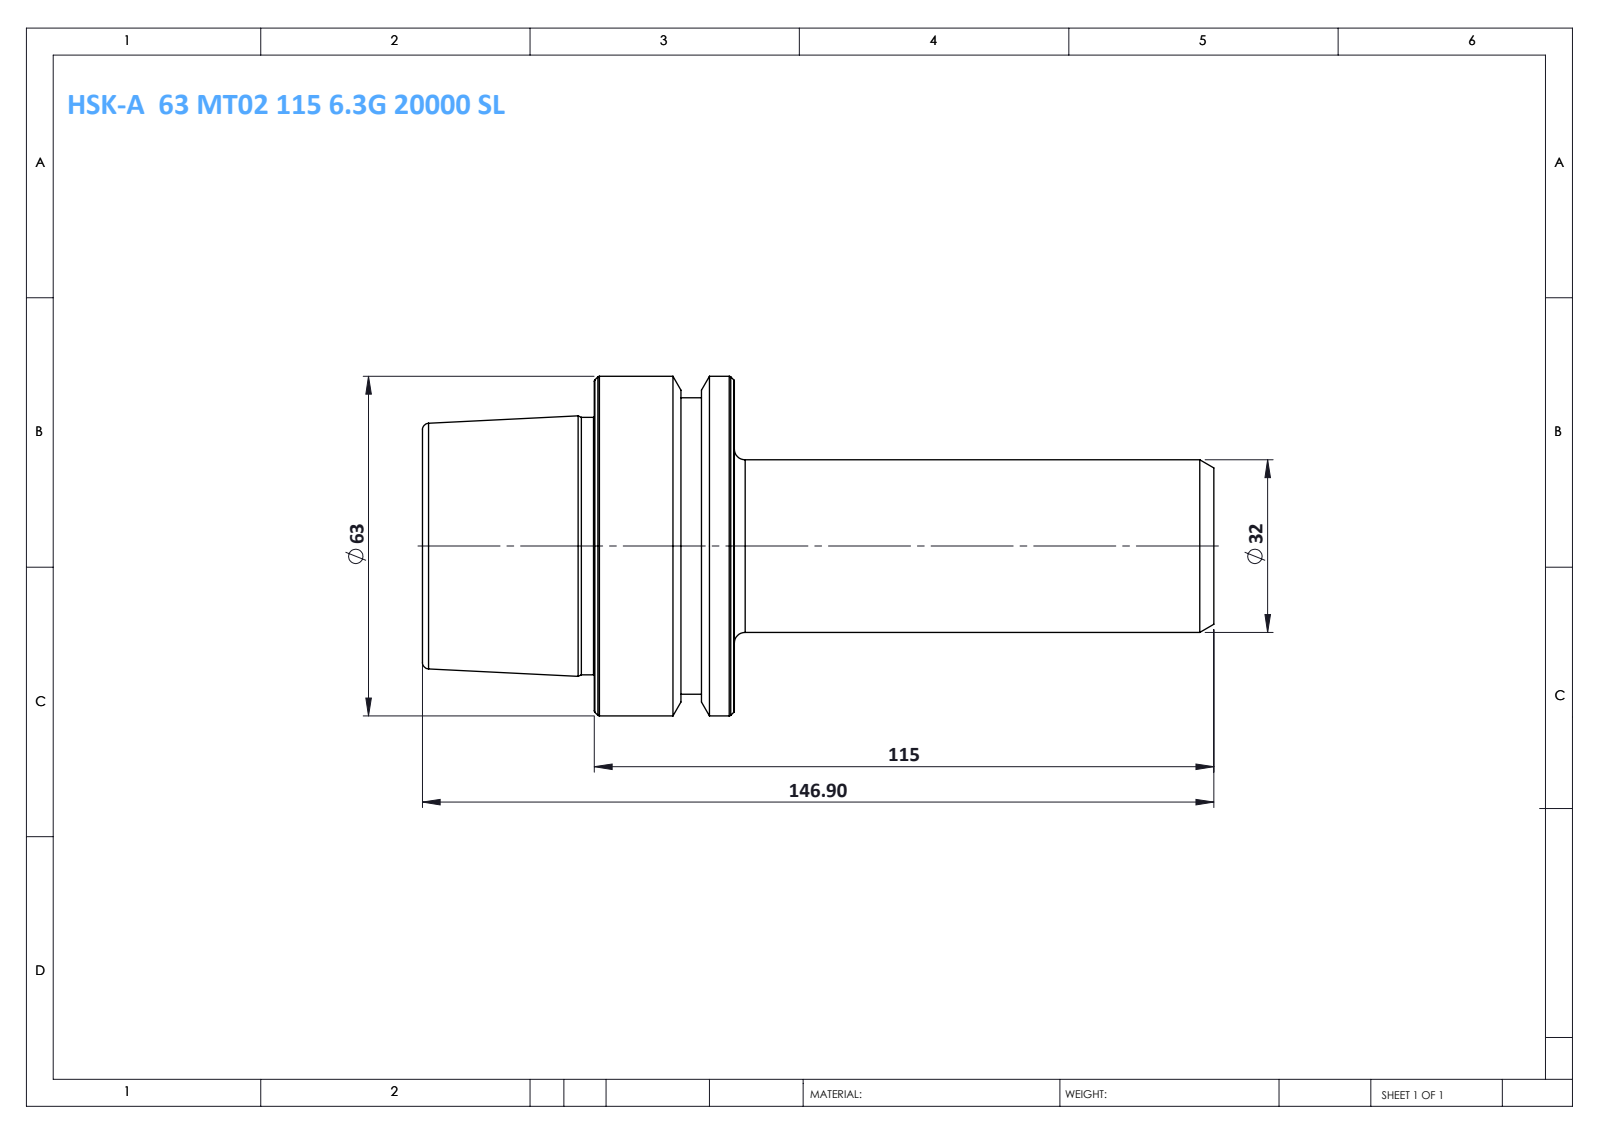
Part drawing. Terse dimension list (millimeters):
name: HSK-A 63 MT02 115 6.3G 20000 SL
written by: SolidWorks 2014 (CONFIG_CONTROL_DESIGN)
unit: mm
bodies: 1 solid, 46 faces (6 planar, 10 cylindrical, 30 other)
size: 146.9 × 63 × 63
volume: 204 049 mm³; area: 25 392 mm²
bosses: 1× ⌀63, 1× ⌀55, 1× ⌀47.78, 1× ⌀32
face distances: 57.9, 26, 31.9, 89, 115, 146.9, 95.1, 6.1, 19.9, 51.8
